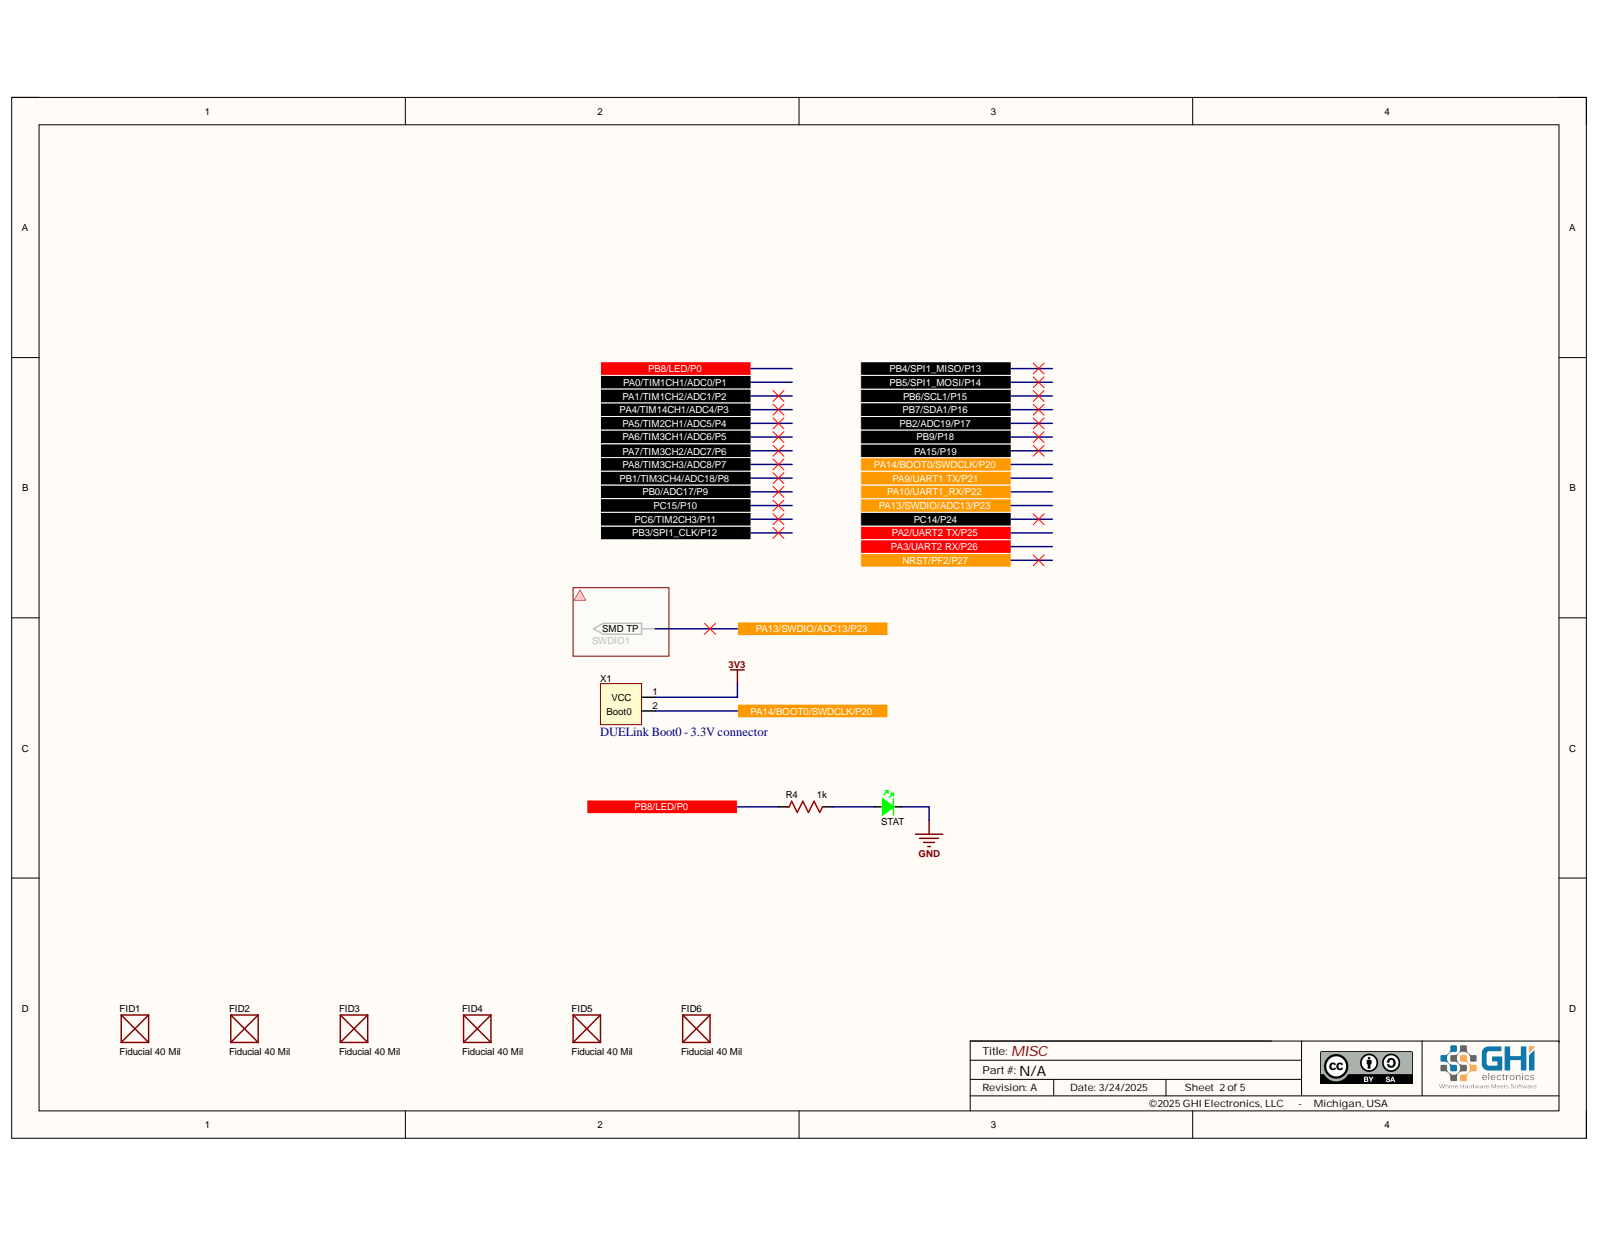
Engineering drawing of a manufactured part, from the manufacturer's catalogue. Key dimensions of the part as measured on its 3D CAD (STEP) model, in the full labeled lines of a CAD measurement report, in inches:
Part name (STEP PRODUCT): PCB; Board; BTN1; Switch_Omron_B3FS-4055P_eec (+7 more)
STEP written by: Open CASCADE 7.5 (AUTOMOTIVE_DESIGN)
Units: inches
Bodies: 94 solids, 1472 faces (1095 planar, 241 cylindrical, 136 other)
Overall size (bounding box): 1.063 × 0.866 × 0.485
Volume: 0.047 in³ · Surface area: 3.706 in²
Round holes (diameter × count): ⌀0.118 ×4, ⌀0.04 ×2, ⌀0.067 ×1, ⌀0.098 ×1, ⌀0.291 ×1
Round bosses / shafts (diameter × count): ⌀0.049 ×4, ⌀0.28 ×1, ⌀0.122 ×1
Partial cylindrical surfaces — rounded edges, fillets, slot ends (radius × count): R0.005 ×35, R0.006 ×14, R0.012 ×8, R0.008 ×4, R0.138 ×4, R0.007 ×2, R0.007 ×2, R0.007 ×2
Main face-to-face distances: 0.154, 0.15, 0.146, 0.161, 0.157, 0.472, 0.142, 0.217, 0.079, 0.039
Hole centre spacings: 0.47, 0.517, 0.591, 0.787, 0.984, 0.1, 0.207, 0.304
